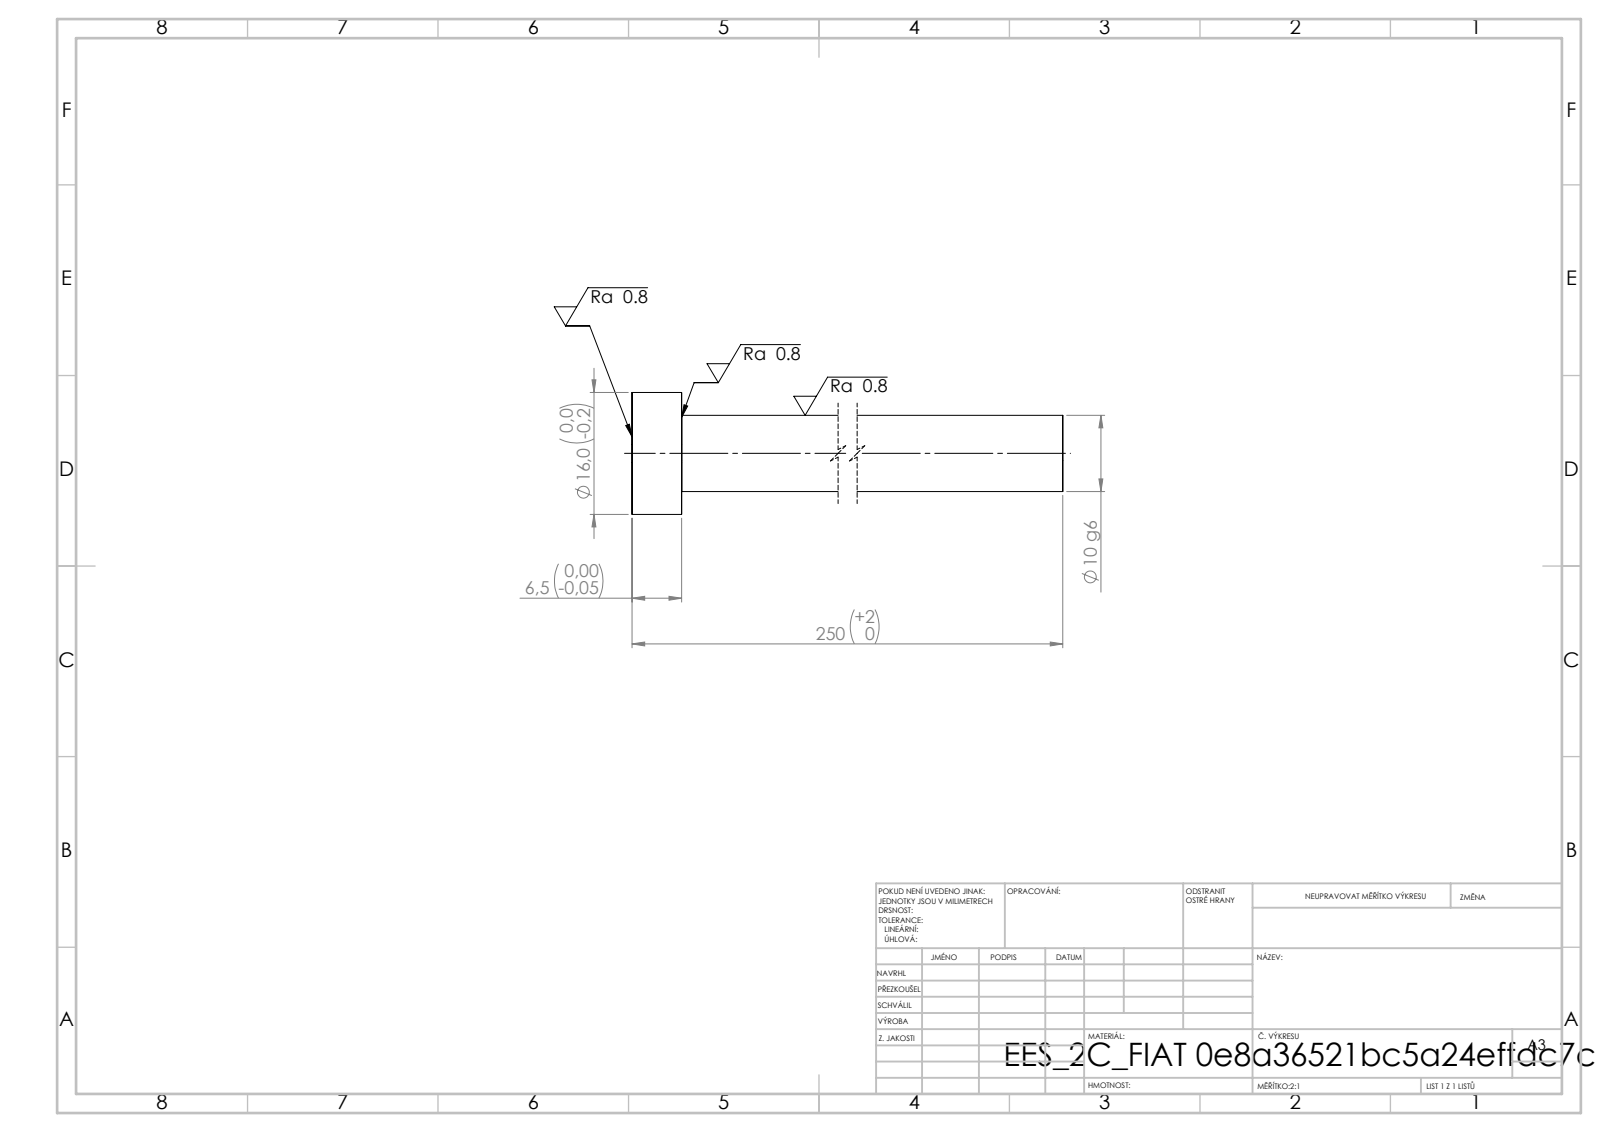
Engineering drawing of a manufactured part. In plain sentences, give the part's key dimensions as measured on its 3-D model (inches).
Its 3-D file was written by "SolidWorks 2019 (CONFIG_CONTROL_DESIGN)". It is 1 solid with 7 faces: 3 planar, 4 cylindrical and 0 other. Overall it measures 9.843 by 0.63 by 0.63 inches. Its volume is 1.247 cubic inches and its surface area 12.99 square inches. Round bosses or shafts: 1 of diameter 0.63, 1 of diameter 0.394. The main face-to-face distances are 0.256, 9.843, 9.587.
